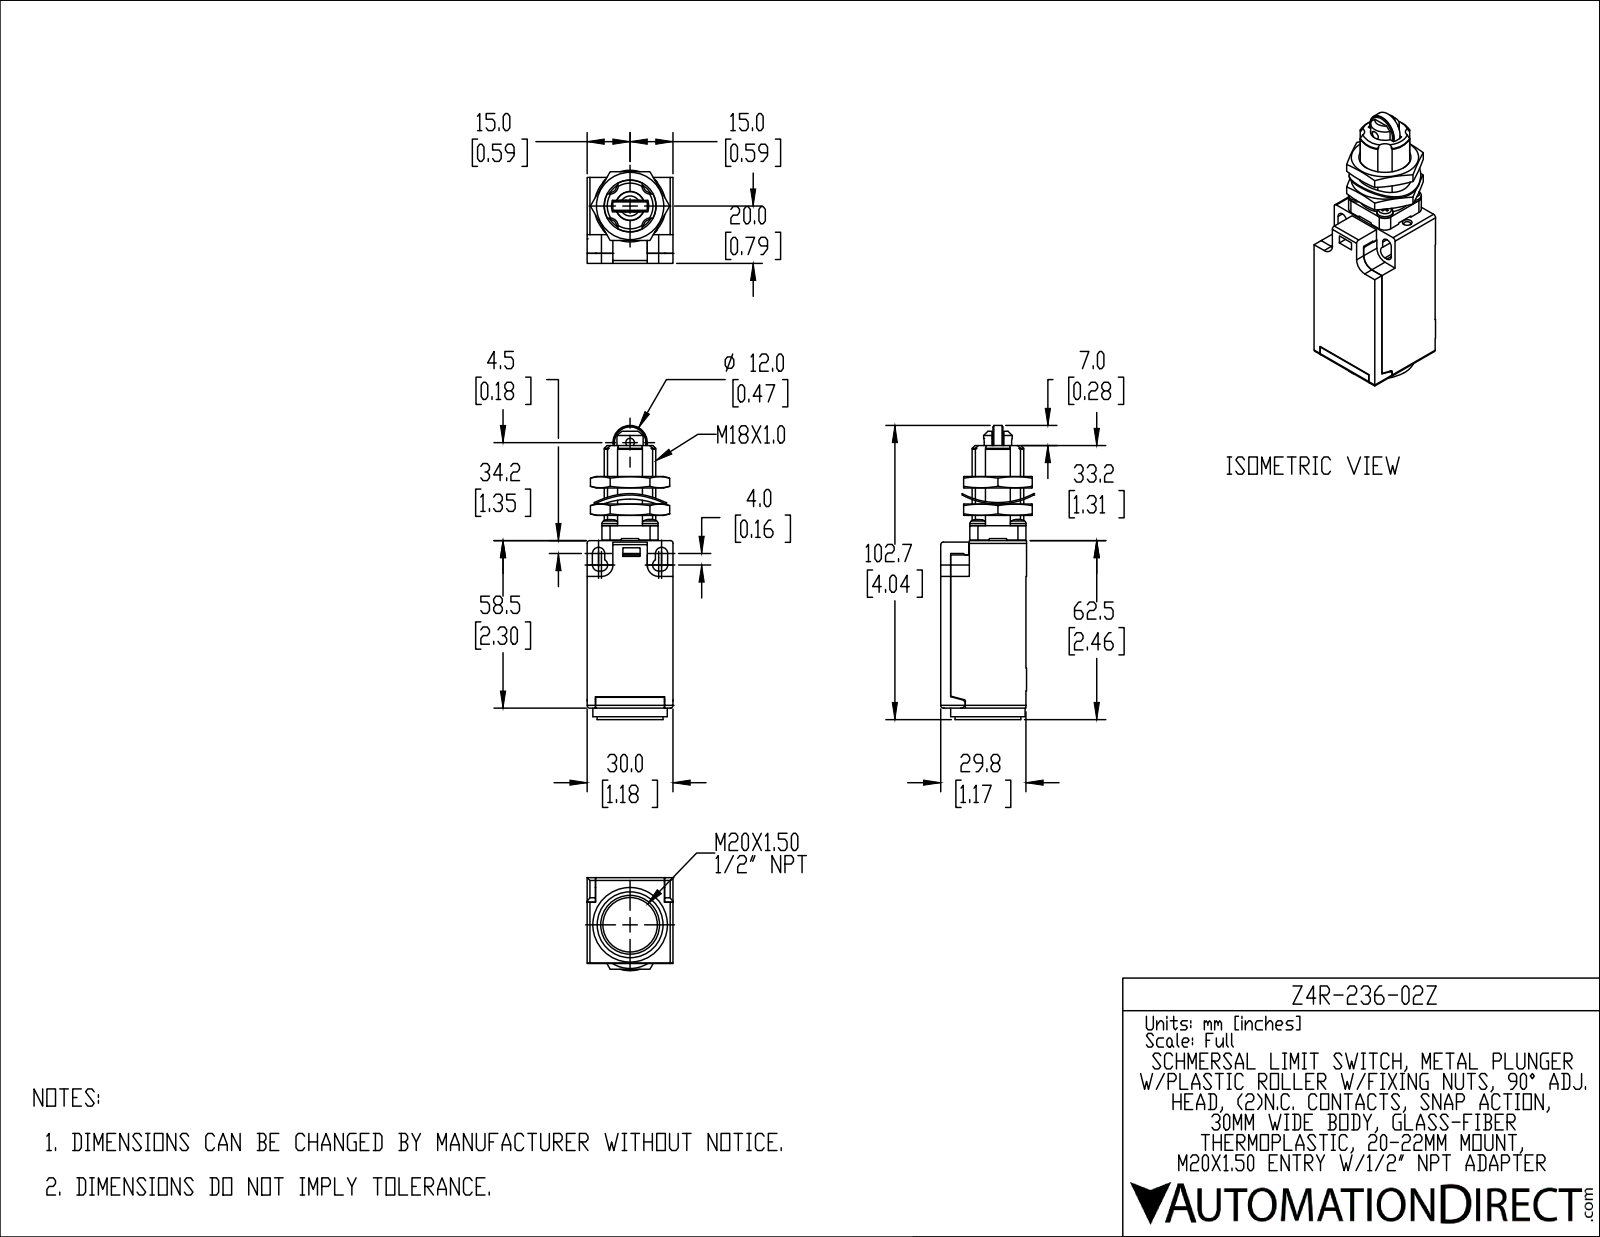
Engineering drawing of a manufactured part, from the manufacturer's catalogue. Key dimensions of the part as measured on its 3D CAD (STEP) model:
Part name (STEP PRODUCT): Z4R-236-02Z
STEP written by: SolidWorks 2019 (AUTOMOTIVE_DESIGN)
Units: inches
Bodies: 4 solids, 370 faces (238 planar, 97 cylindrical, 35 other)
Overall size (bounding box): 4.043 × 1.279 × 1.181
Volume: 3.517 in³ · Surface area: 32 in²
Round holes (diameter × count): ⌀0.094 ×6, ⌀0.126 ×4, ⌀0.118 ×1, ⌀0.512 ×1, ⌀0.545 ×1, ⌀0.732 ×1, ⌀0.748 ×1
Round bosses / shafts (diameter × count): ⌀0.213 ×4, ⌀1.024 ×1, ⌀0.984 ×1, ⌀0.906 ×1, ⌀0.472 ×1, ⌀0.415 ×1, ⌀0.394 ×1, ⌀0.276 ×1
Partial cylindrical surfaces — rounded edges, fillets, slot ends (radius × count): R0.039 ×6, R0.085 ×6, R0.11 ×4, R0.11 ×4, R0.157 ×2, R1.043 ×2, R0.024 ×1, R0.059 ×1
Main face-to-face distances: 1.181, 0.138, 1.035, 1.173, 0.157, 1.043, 0.087, 0.079, 2.067, 0.118
Hole centre spacings: 0.317, 0.39, 0.551, 0.76, 0.308, 0.433, 0.454, 0.497
